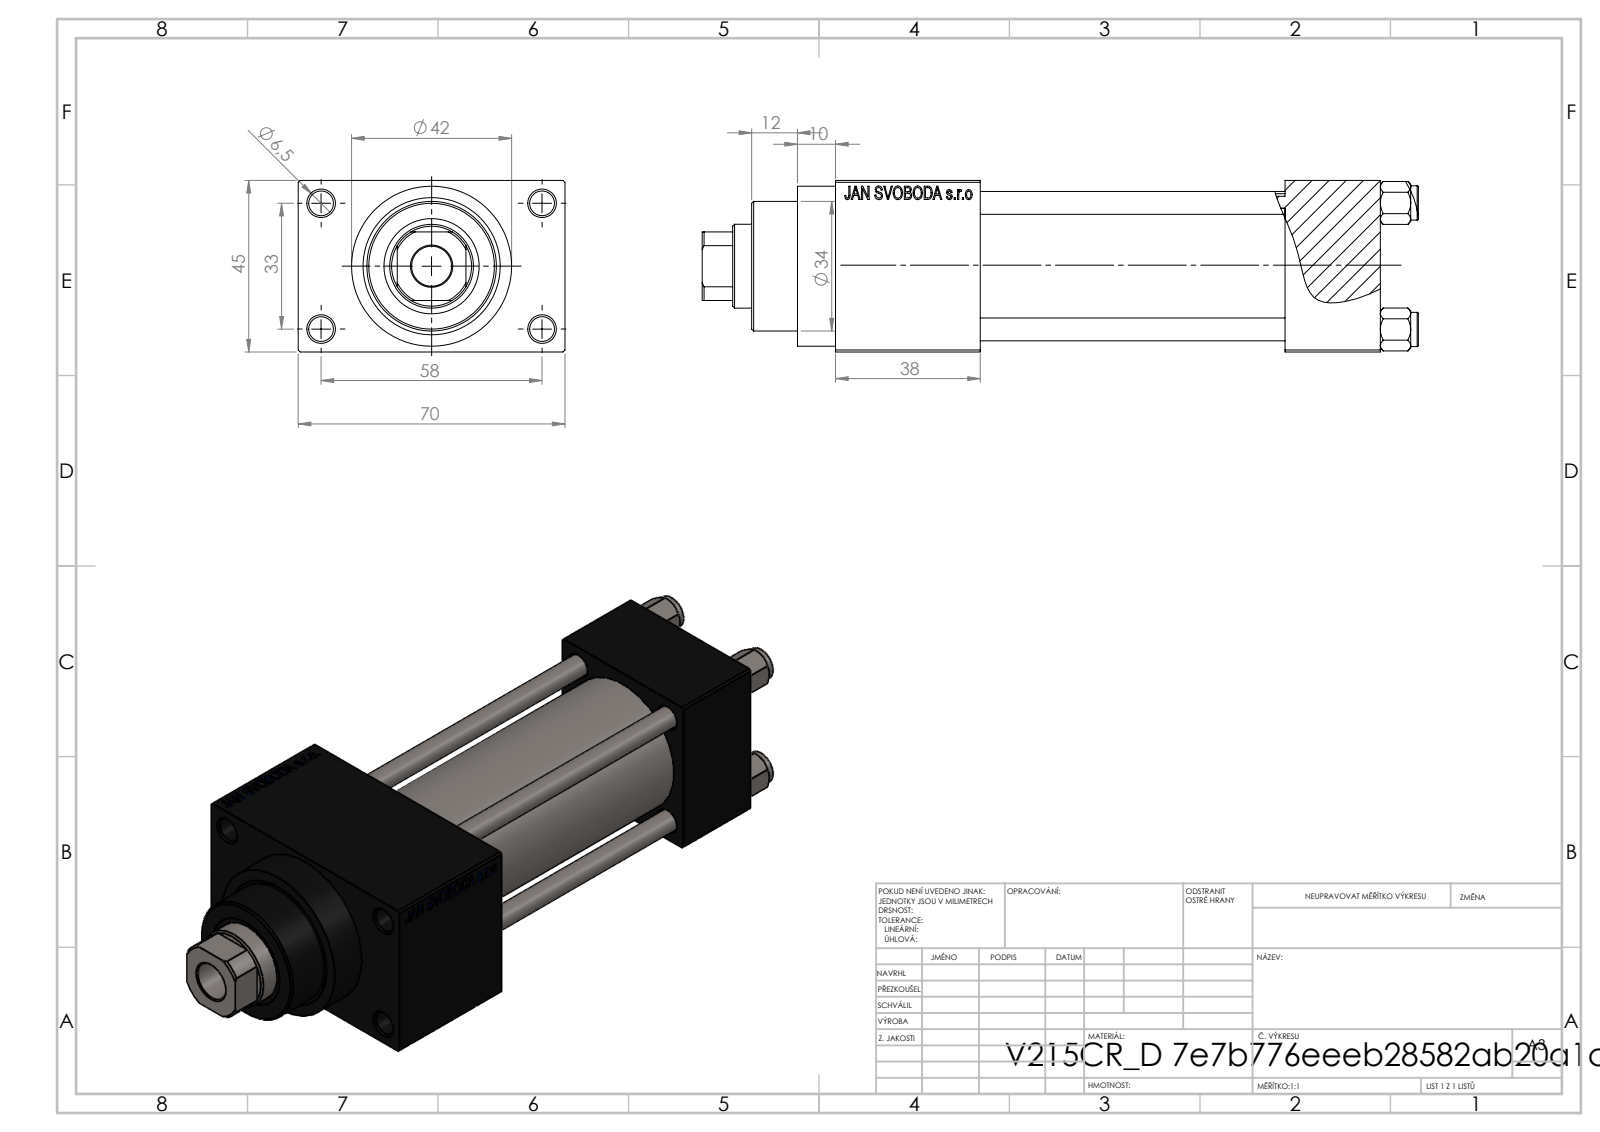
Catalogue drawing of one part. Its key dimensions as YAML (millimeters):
part_name: "NUT_M5_D; V215CR_VCP_D; V215CR_D_TYCINKA; V215_VC_A (+1 more)"
step_written_by: "SolidWorks 2019 (CONFIG_CONTROL_DESIGN)"
units: millimeters
bodies: {solids: 11, faces: 1104, planar: 496, cylindrical: 88, other: 520}
overall_size: [188, 70, 45]
volume: 267569
surface_area: 90817
round_holes:
  - {diameter: 6, count: 4}
  - {diameter: 6.5, count: 4}
  - {diameter: 7, count: 2}
  - {diameter: 13.16, count: 2}
  - {diameter: 20, count: 2}
  - {diameter: 10.5, count: 1}
  - {diameter: 22, count: 1}
  - {diameter: 24, count: 1}
  - {diameter: 25, count: 1}
  - {diameter: 32, count: 1}
  - {diameter: 33, count: 1}
round_bosses_or_shafts:
  - {diameter: 9, count: 4}
  - {diameter: 42, count: 1}
  - {diameter: 38, count: 1}
  - {diameter: 34, count: 1}
partial_cylinders:
  - {radius: 10.5, count: 1}
face_to_face_distances: [45, 25, 12.5, 80, 105, 57.5, 118, 38, 143, 70]
hole_center_spacings: [12.4, 23.48, 33.2, 33.37, 35.35, 45.6, 56.35, 33]
